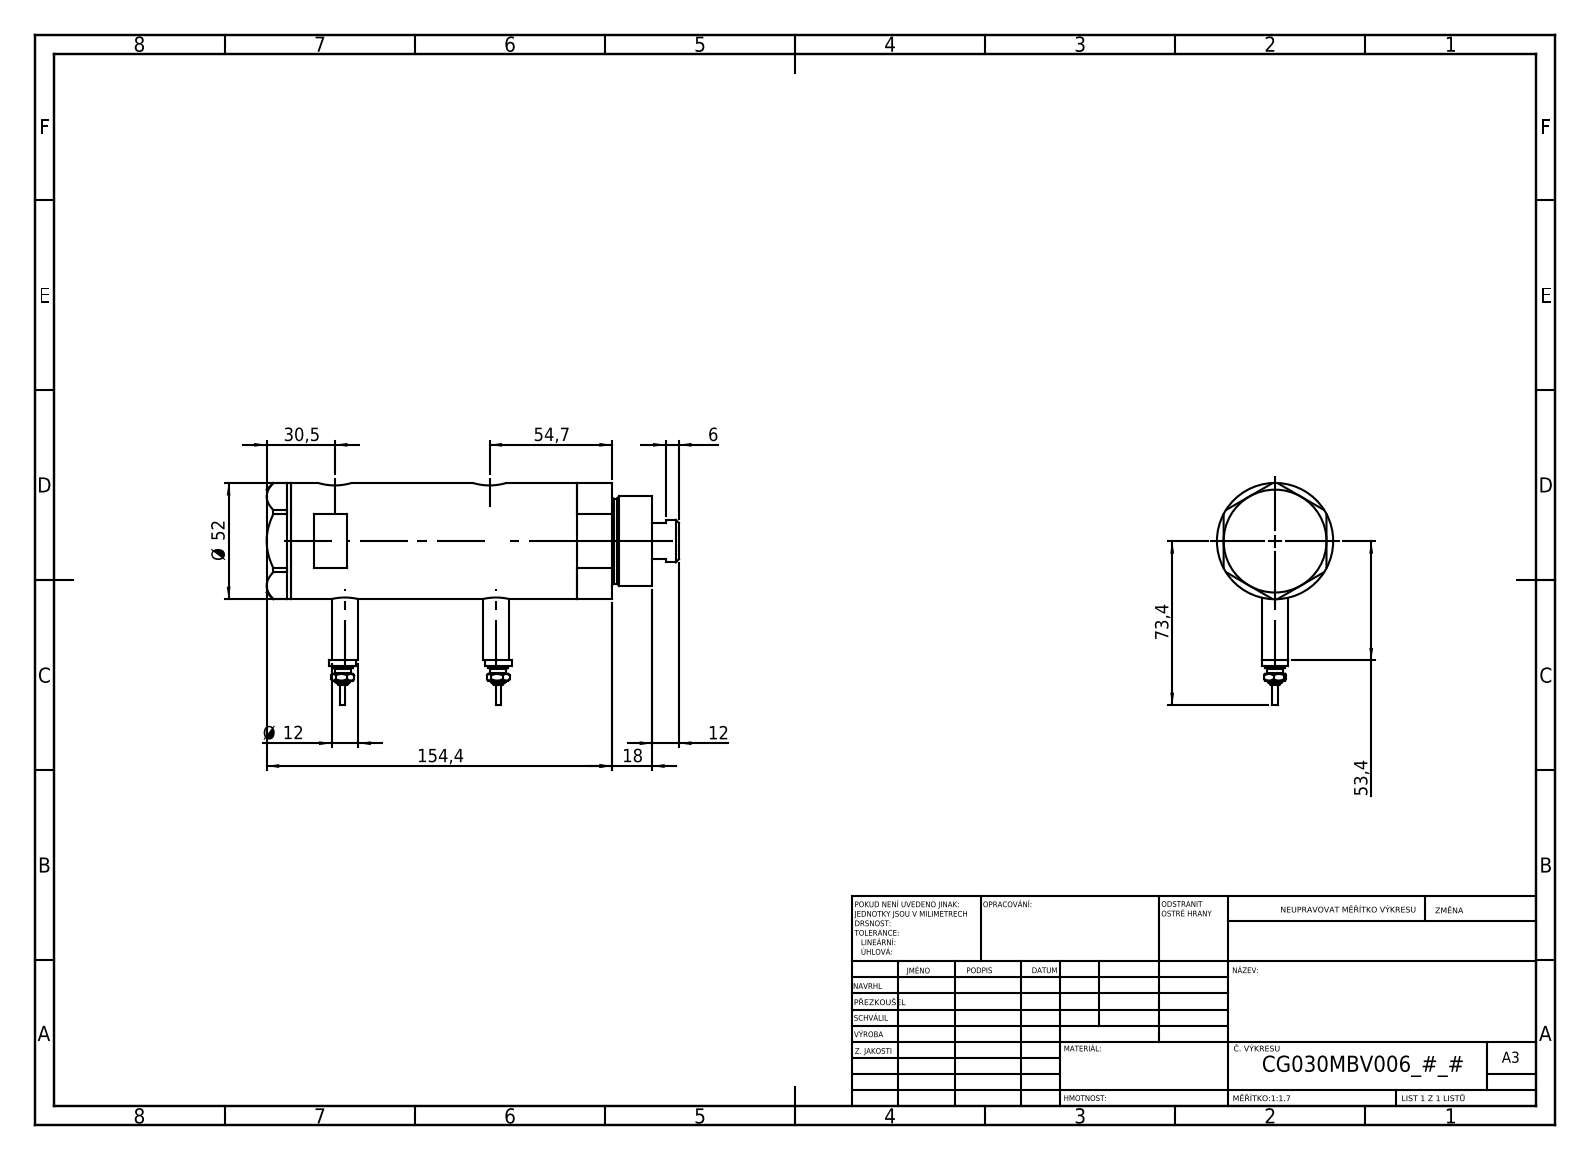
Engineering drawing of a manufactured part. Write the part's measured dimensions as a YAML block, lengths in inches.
part_name: "Switch; V270CG_VC; V270CG_FRONT; V270CG_BACK (+1 more)"
step_written_by: "SolidWorks 2019 (CONFIG_CONTROL_DESIGN)"
units: inches
bodies: {solids: 6, faces: 226, planar: 93, cylindrical: 69, other: 64}
overall_size: [7.26, 3.913, 2.047]
volume: 21.38
surface_area: 125
round_holes:
  - {diameter: 0.383, count: 2}
  - {diameter: 0.492, count: 2}
  - {diameter: 0.591, count: 2}
  - {diameter: 0.256, count: 1}
  - {diameter: 0.787, count: 1}
  - {diameter: 0.846, count: 1}
  - {diameter: 1.181, count: 1}
  - {diameter: 1.299, count: 1}
  - {diameter: 1.732, count: 1}
round_bosses_or_shafts:
  - {diameter: 0.472, count: 4}
  - {diameter: 0.354, count: 2}
  - {diameter: 0.276, count: 2}
  - {diameter: 0.177, count: 2}
  - {diameter: 0.098, count: 2}
  - {diameter: 2.047, count: 1}
  - {diameter: 1.575, count: 1}
  - {diameter: 1.496, count: 1}
face_to_face_distances: [3.602, 0.937, 2.665, 0.433, 1.37, 4.035, 1.811, 1.433, 5.469, 5.035]
hole_center_spacings: [0.114, 0.177, 2.547, 2.661, 2.724, 2.839]
